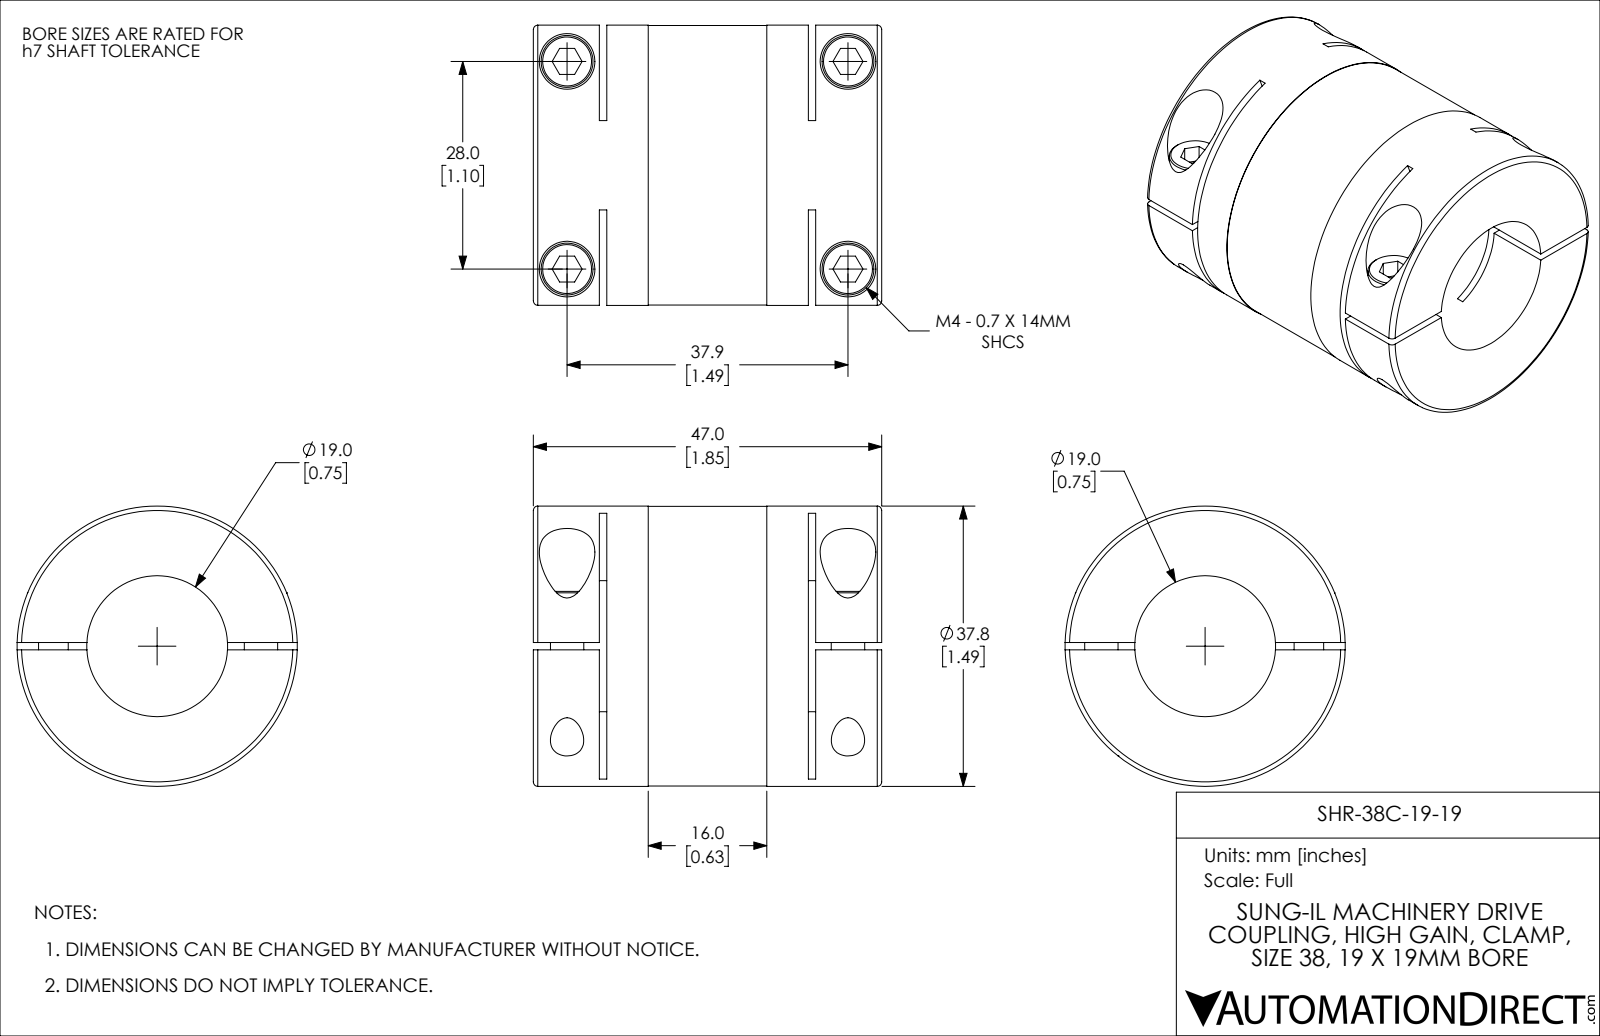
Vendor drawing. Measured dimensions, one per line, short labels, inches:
name: SHR-38C-19-19
written by: SolidWorks 2021 (CONFIG_CONTROL_DESIGN)
unit: in
bodies: 1 solid, 144 faces (70 planar, 58 cylindrical, 16 other)
size: 1.85 × 1.488 × 1.488
volume: 2.157 in³; area: 23.34 in²
holes: 4× ⌀0.177, 4× ⌀0.295, 1× ⌀0.748, 1× ⌀0.827
bosses: 4× ⌀0.276, 2× ⌀0.157, 1× ⌀1.488, 1× ⌀1.484
rounds: 2× R1.969
face distances: 0.039, 0.39, 1.461, 0.35, 1.5, 1.11, 1.85, 1.071, 1.15, 1.24
hole spacings: 1.102, 1.492, 1.855
